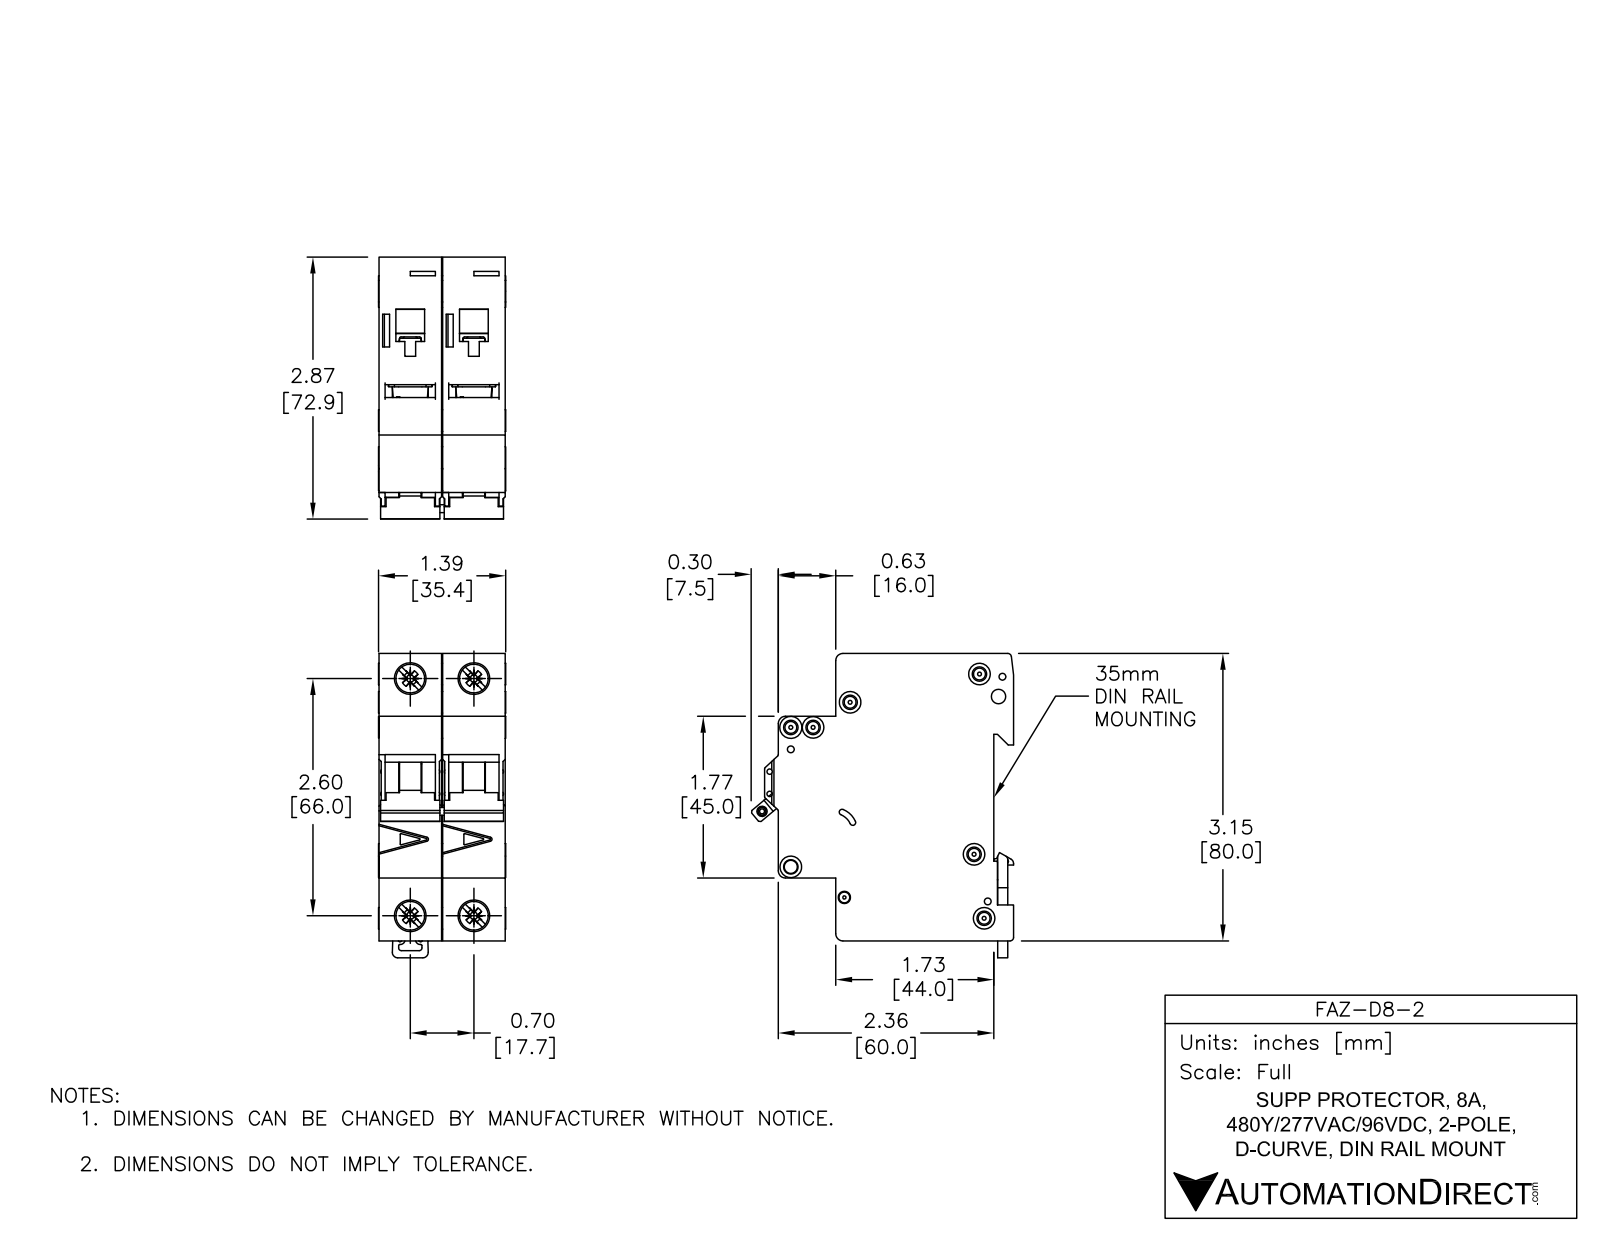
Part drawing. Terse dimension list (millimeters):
name: FAZ-D8-2
written by: SolidWorks 2014 (AUTOMOTIVE_DESIGN)
unit: mm
bodies: 8 solids, 1104 faces (466 planar, 396 cylindrical, 242 other)
size: 84.78 × 73.04 × 35.4
volume: 149 808 mm³; area: 38 799 mm²
holes: 6× ⌀3.6, 3× ⌀1.9, 2× ⌀1.09, 2× ⌀1.5, 2× ⌀4, 2× ⌀7.15, 2× ⌀8.2, 1× ⌀2.15, 1× ⌀2.2, 1× ⌀2.55, 1× ⌀3.3, 1× ⌀3.4
bosses: 4× ⌀6, 2× ⌀8.2, 2× ⌀2.5
rounds: 49× R0.25, 19× R0.5, 10× R2, 8× R0.2, 8× R1, 2× R0.8, 2× R1.8, 2× R3
face distances: 17.7, 17.5, 35.2, 79.48, 5.5, 49.5, 44, 65.5, 60, 16
hole spacings: 6.2, 13.64, 17.7, 66, 68.33, 4.81, 5.19, 5.61
